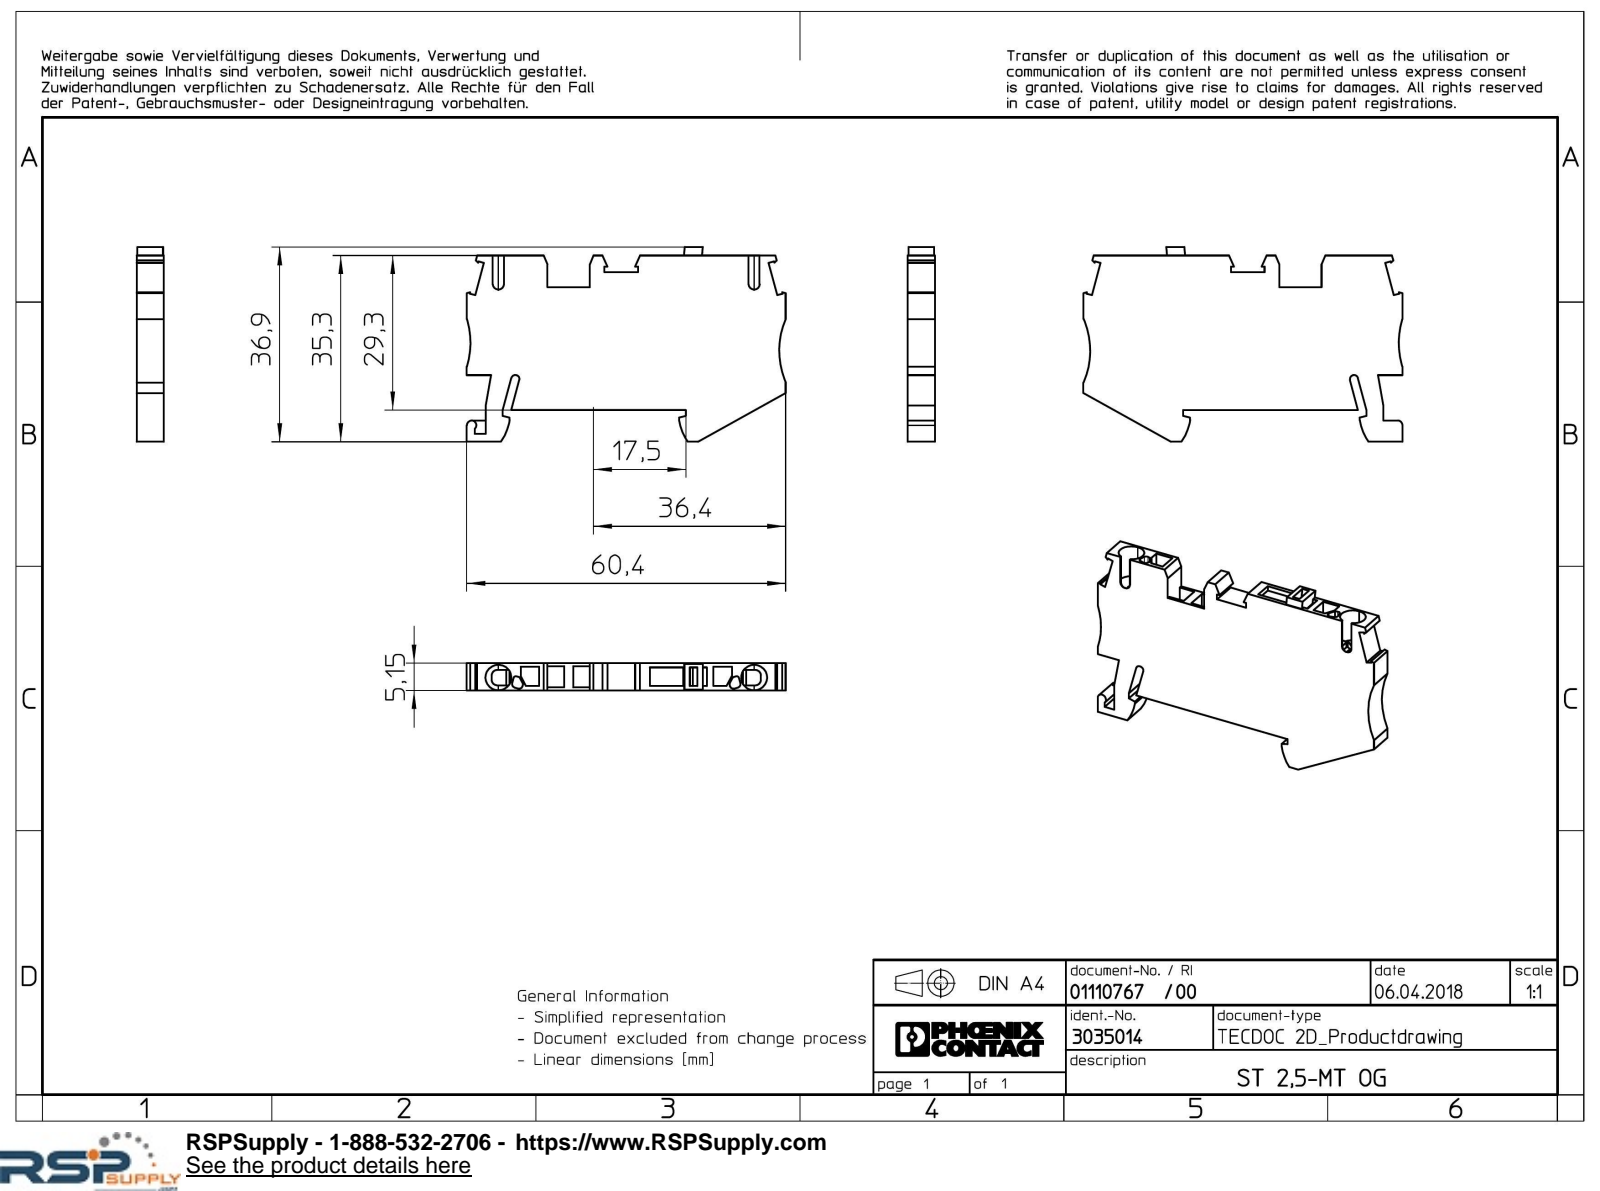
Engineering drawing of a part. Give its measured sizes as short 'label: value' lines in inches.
name: ST_2.5_MT_OG-select
written by: Creo Elements/Direct Modeling 18.1I 14-Aug-2016 (C) Parametric Technology GmbH (AUTOMOTIVE_DESIGN)
unit: in
bodies: 1 solid, 172 faces (131 planar, 31 cylindrical, 10 other)
size: 2.378 × 1.451 × 0.203
volume: 0.47 in³; area: 8.942 in²
rounds: 8× R0.039, 4× R0.012, 4× R0.094, 2× R0.02, 2× R0.024, 2× R0.026, 2× R0.374, 2× R0.47
face distances: 0.203, 1.152, 0.191, 0.026, 0.124, 0.157, 0.023, 0.18, 0.18, 0.022
